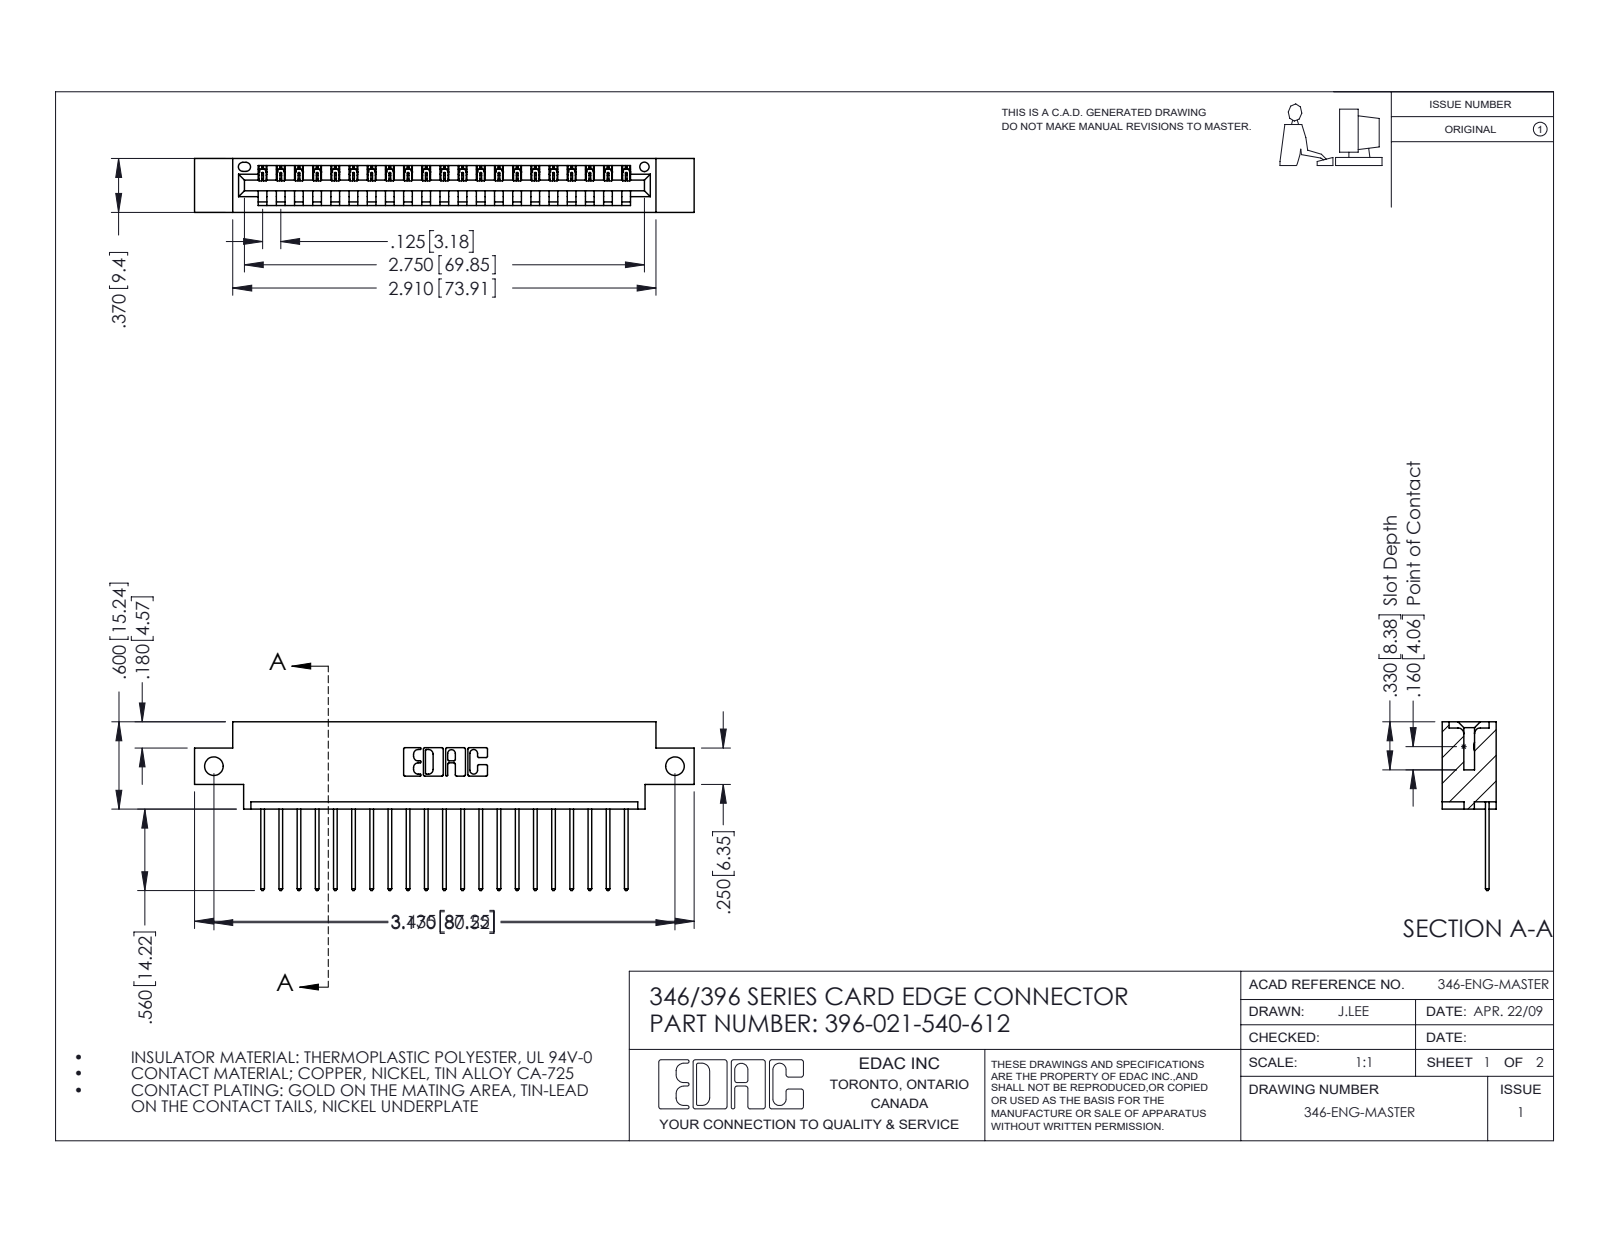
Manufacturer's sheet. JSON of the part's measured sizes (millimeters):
{"part_name": "346 Part_0.170 Offset - Side Mount; 345-292-001_345-293-140; 396-021-540-612", "step_written_by": "SolidWorks 2016 (CONFIG_CONTROL_DESIGN)", "units": "millimeters", "bodies": {"solids": 22, "faces": 1344, "planar": 920, "cylindrical": 424, "other": 0}, "overall_size": [87.2, 29.5, 9.4], "volume_mm3": 8000, "surface_area_mm2": 9987, "round_holes": [[3.3, 2], [1.6, 1]], "partial_cylinders_radius": [[0.2, 42], [0.3, 42], [0.3, 22], [0.2, 6], [0.8, 6], [0.7, 3], [0.8, 2], [1, 2]], "face_to_face_distances": [1.2, 8.2, 9.4, 6.4, 1.8, 7.6, 0.6, 3.8, 5.6, 2.5], "hole_center_spacings": [80.5]}
